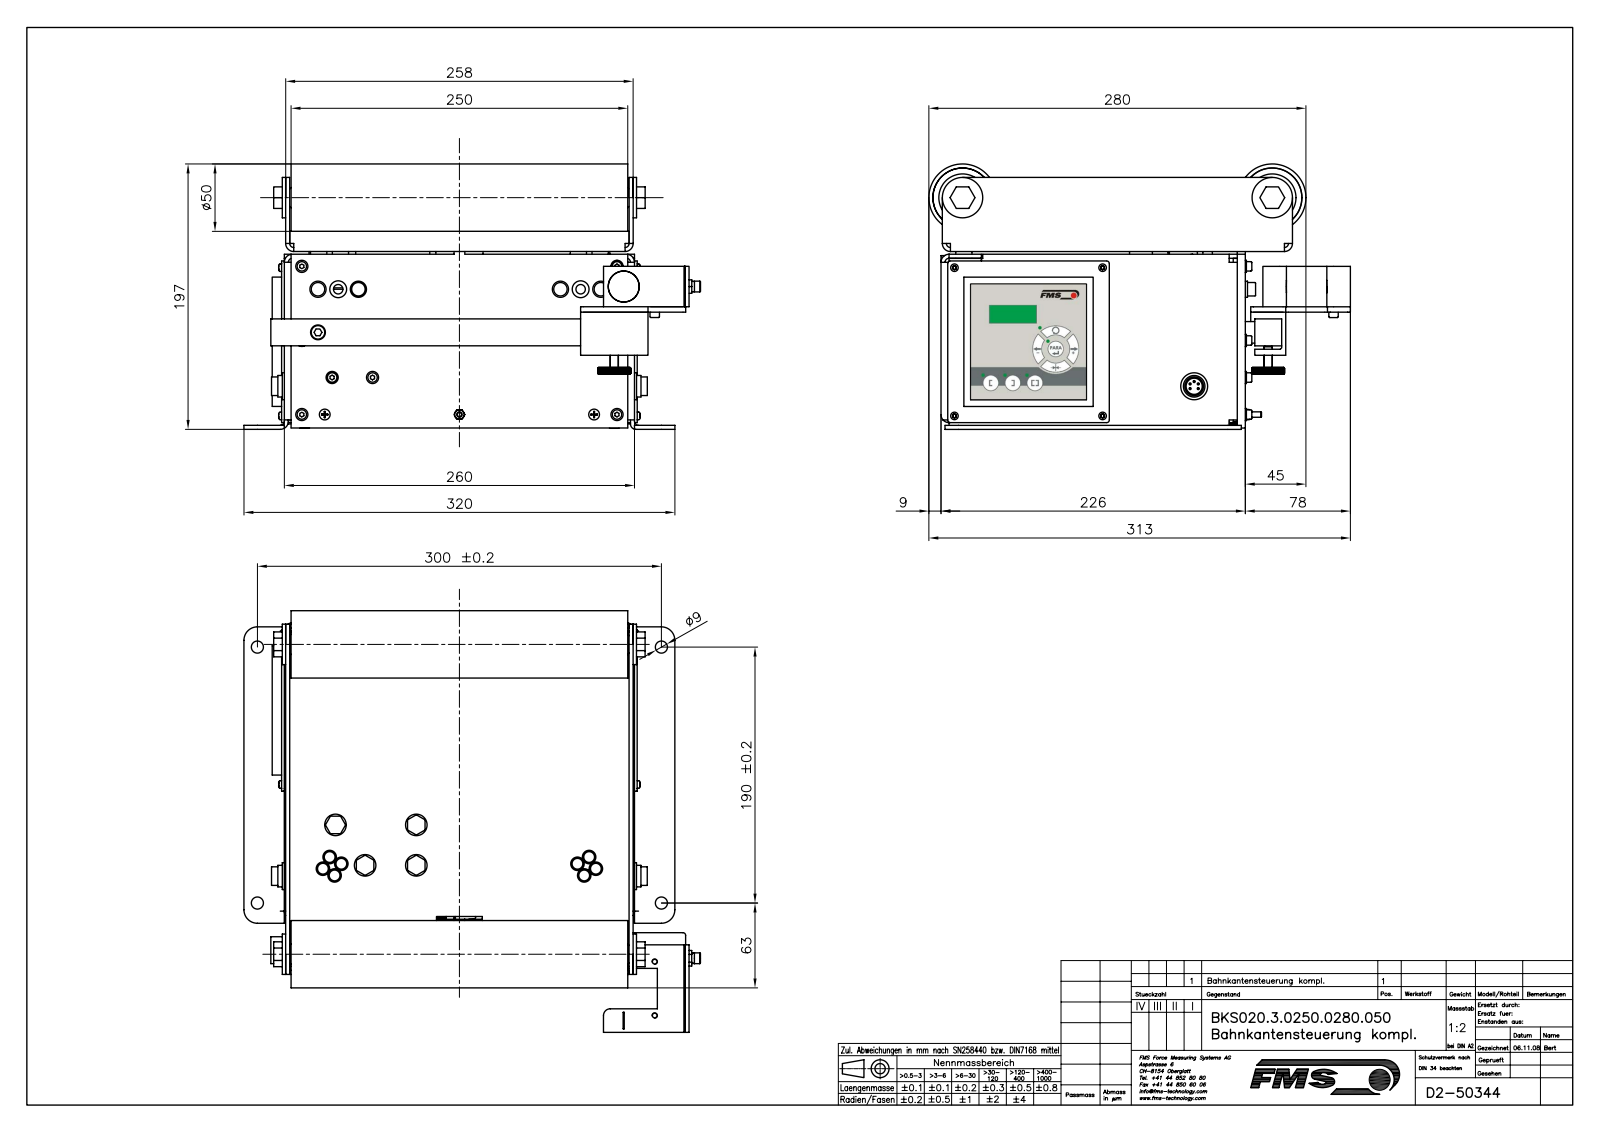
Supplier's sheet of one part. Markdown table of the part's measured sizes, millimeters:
| quantity | value |
| --- | --- |
| part name | K50344; K49821; K49822; TEIL1 (+8 more) |
| STEP written by | Mechanical Desktop 2007 (CONFIG_CONTROL_DESIGN) |
| units | millimeters |
| bodies | 159 solids, 5852 faces (3611 planar, 1777 cylindrical, 464 other) |
| overall size | 339.1 × 313 × 197 |
| volume | 1 804 000 mm³ |
| surface area | 1 172 000 mm² |
| round holes (diameter × count) | 3 × 30, 4.3 × 14, 3.42 × 13, 3.2 × 9, 2.2 × 8, 2.6 × 8, 5.3 × 8, 6.4 × 8, 3.5 × 7, 6 × 6, 8.4 × 6, 1 × 4 |
| round bosses / shafts (diameter × count) | 10 × 18, 4 × 18, 8 × 15, 6 × 11, 7 × 10, 12 × 8, 9 × 8, 5 × 8 |
| partial cylindrical surfaces (radius × count) | 0.32 × 48, 1 × 29, 0.25 × 24, 2 × 24, 0.2 × 20, 0.25 × 19, 3 × 14, 6 × 13 |
| main face-to-face distances | 3, 1, 2, 127, 5, 130, 6, 4, 256, 128 |
| hole center spacings | 10, 83.5, 97.44, 97.87, 15, 30, 110, 184.07 |
